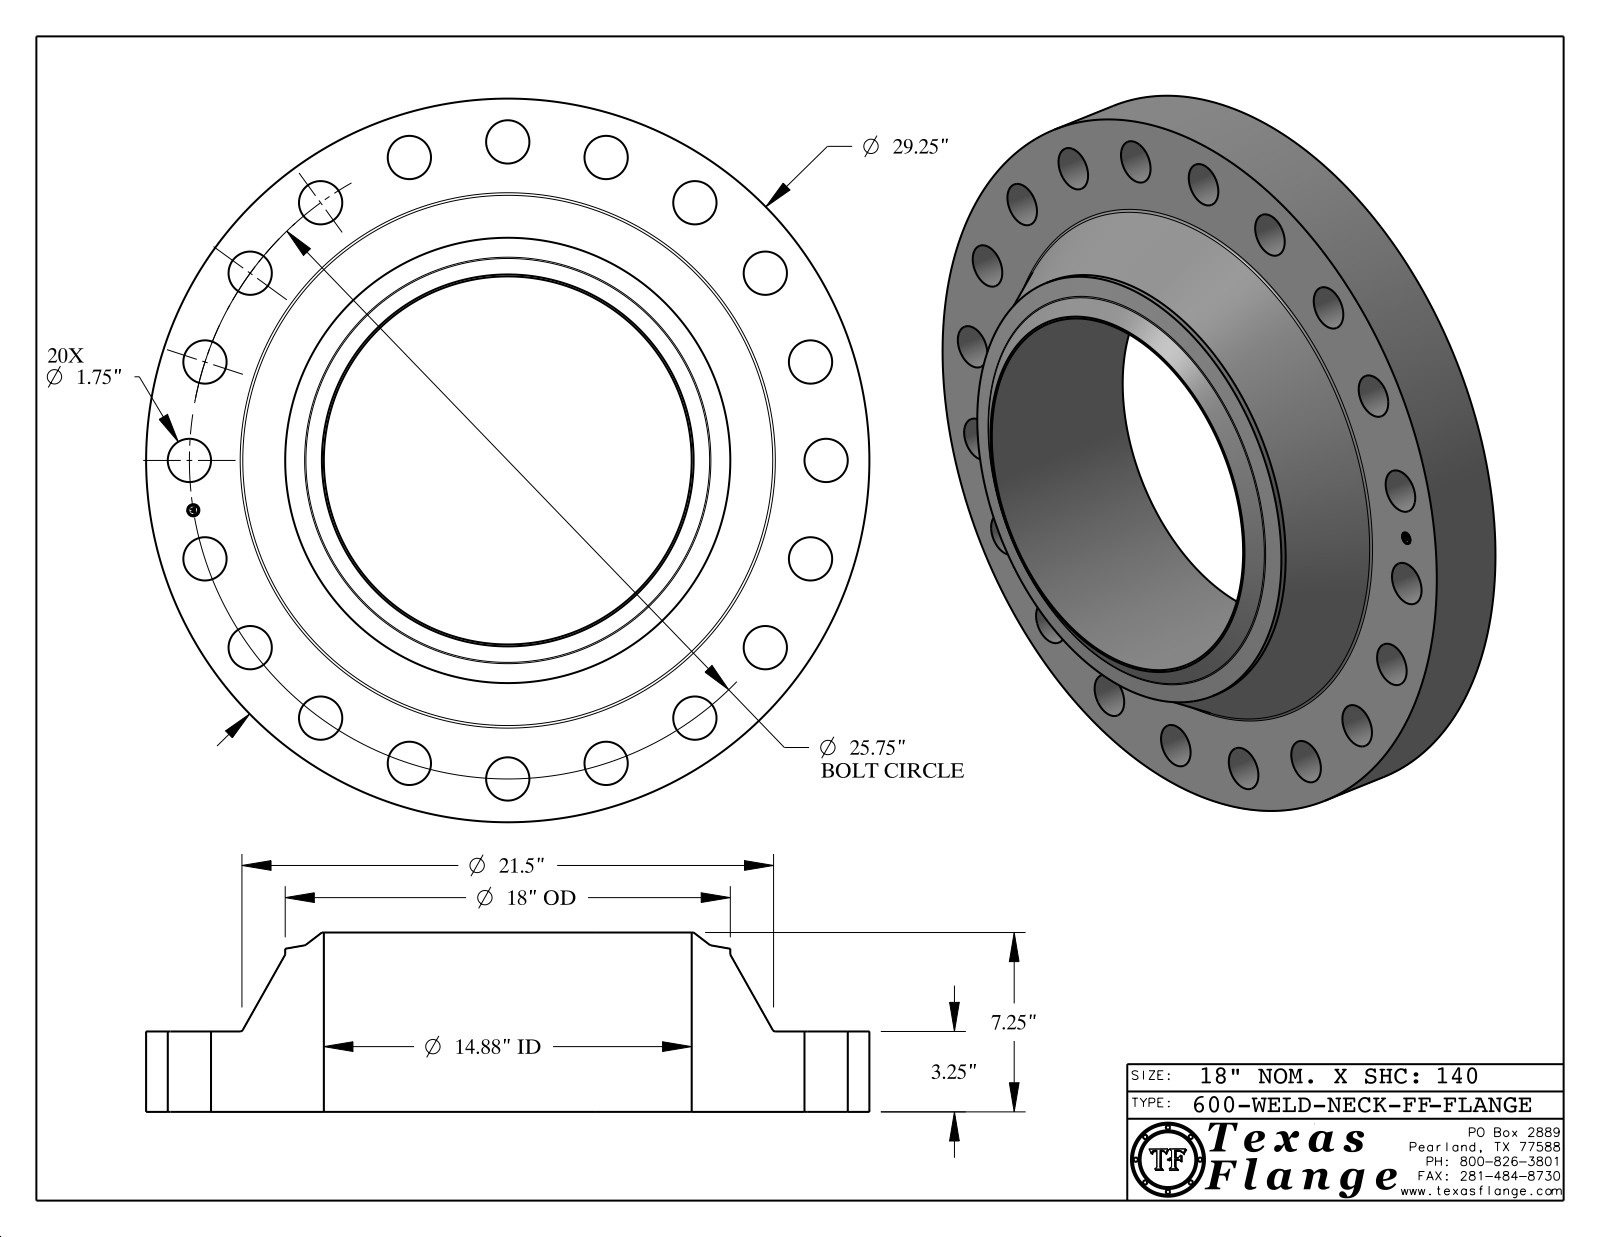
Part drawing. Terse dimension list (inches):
name: 600-WELD-NECK-FF
written by: CATIA V5 STEP AP214 (AUTOMOTIVE_DESIGN)
unit: in
bodies: 1 solid, 444 faces (368 planar, 66 cylindrical, 10 other)
size: 29.25 × 29.25 × 7.25
volume: 1 915 in³; area: 2 029 in²
holes: 20× ⌀1.75, 1× ⌀0.495, 1× ⌀14.876
bosses: 8× ⌀0.03, 1× ⌀29.25, 1× ⌀18, 1× ⌀0.39
face distances: 3.25, 7.25, 4, 0.015, 3.235, 4.015, 0.148, 0.145, 0.027, 0.096
hole spacings: 12.875, 24.49, 25.433, 7.957, 11.691, 4.028, 15.135, 18.208
